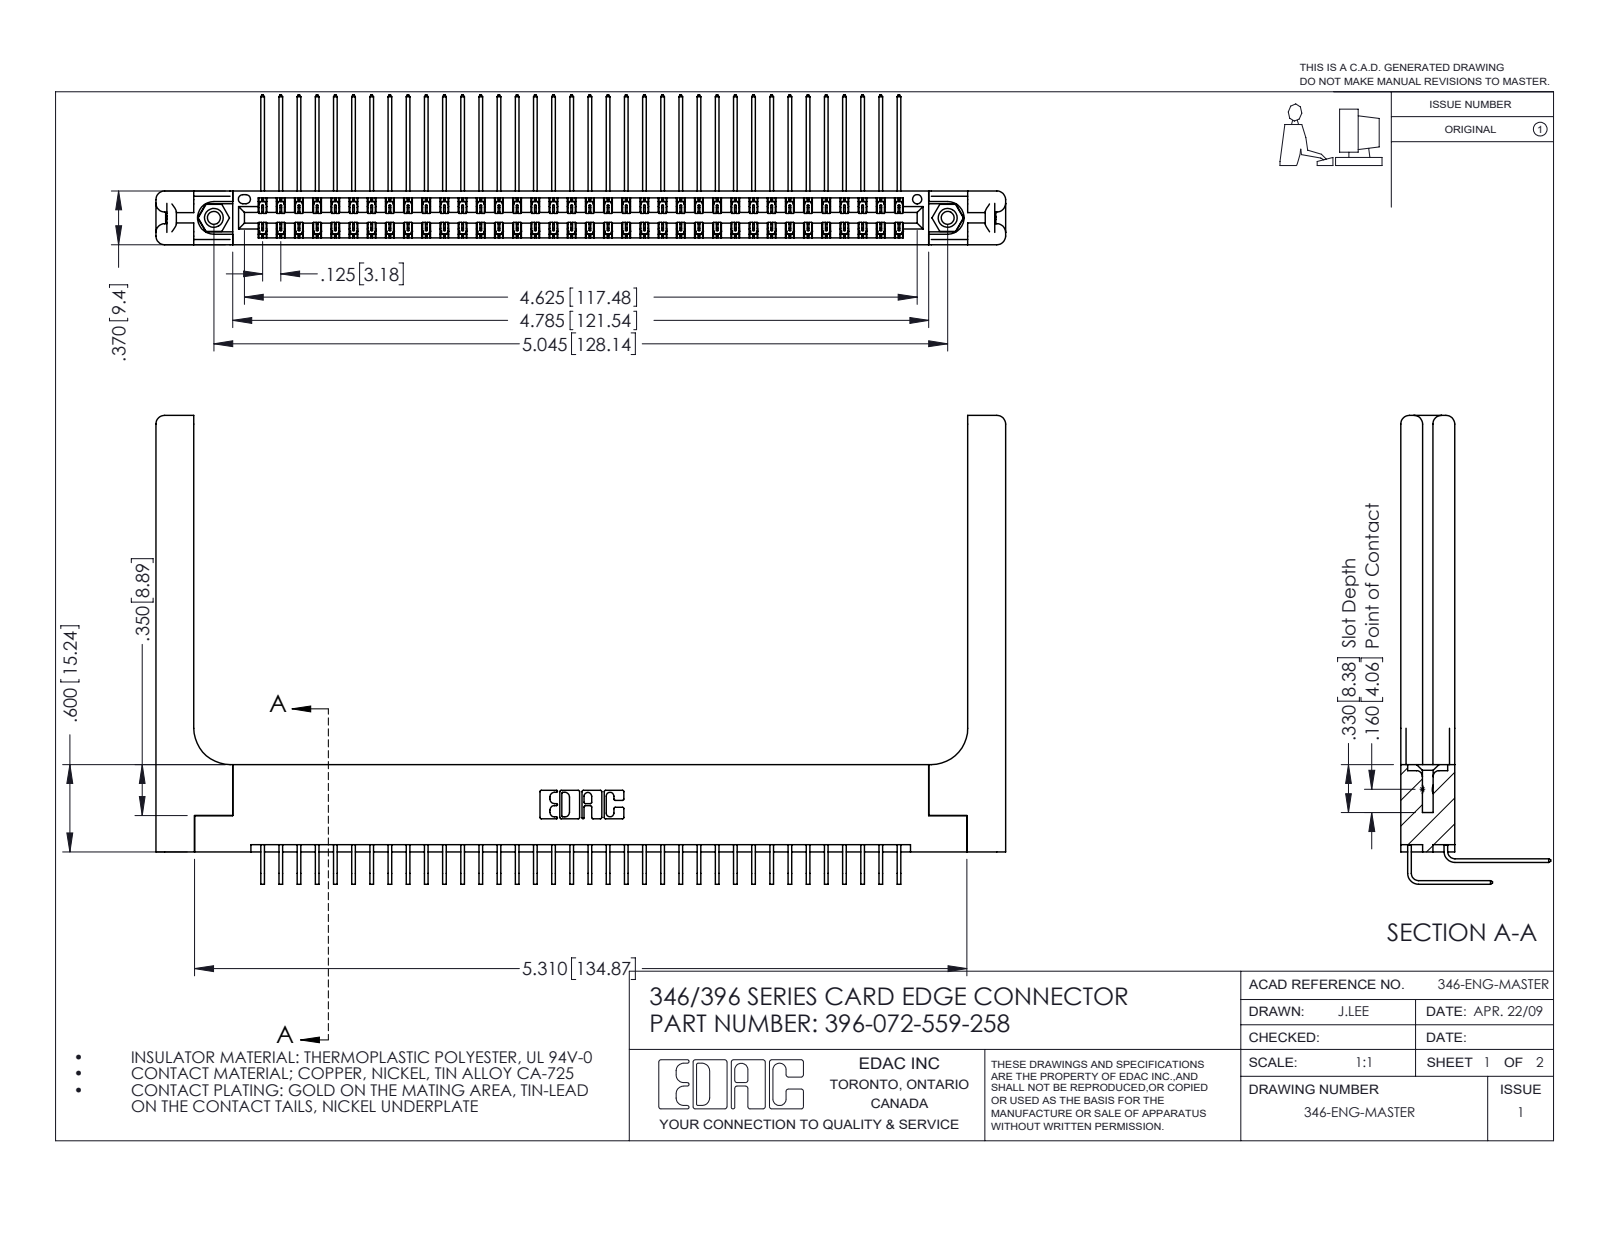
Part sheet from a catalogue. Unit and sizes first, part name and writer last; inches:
Units: inches
Overall size (bounding box): 5.841 × 3.223 × 1.03
Round holes (diameter × count): ⌀0.089 ×2, ⌀0.125 ×2, ⌀0.156 ×2, ⌀0.064 ×1
Round bosses / shafts (diameter × count): ⌀0.155 ×2
Partial cylindrical surfaces — rounded edges, fillets, slot ends (radius × count): R0.006 ×108, R0.01 ×22, R0.06 ×16, R0.007 ×6, R0.031 ×6, R0.026 ×3, R0.014 ×2, R0.022 ×2
Main face-to-face distances: 0.048, 0.37, 0.322, 0.072, 0.025, 0.148, 0.15, 0.25, 0.298, 0.275
Hole centre spacings: 0.246, 4.836, 5.045
Volume: 1.363 in³ · Surface area: 42.26 in²
Bodies: 77 solids, 4266 faces (2888 planar, 1318 cylindrical, 60 other)
Part name (STEP PRODUCT): 346-220-058_345-220-058; 345-292-001_559 Tail - 2; 345-292-001_558 559 Tail - 1; 346 Part_Flush Mounting Lugs - 0.156 Dia-TH (+2 more)
STEP written by: SolidWorks 2016 (CONFIG_CONTROL_DESIGN)
